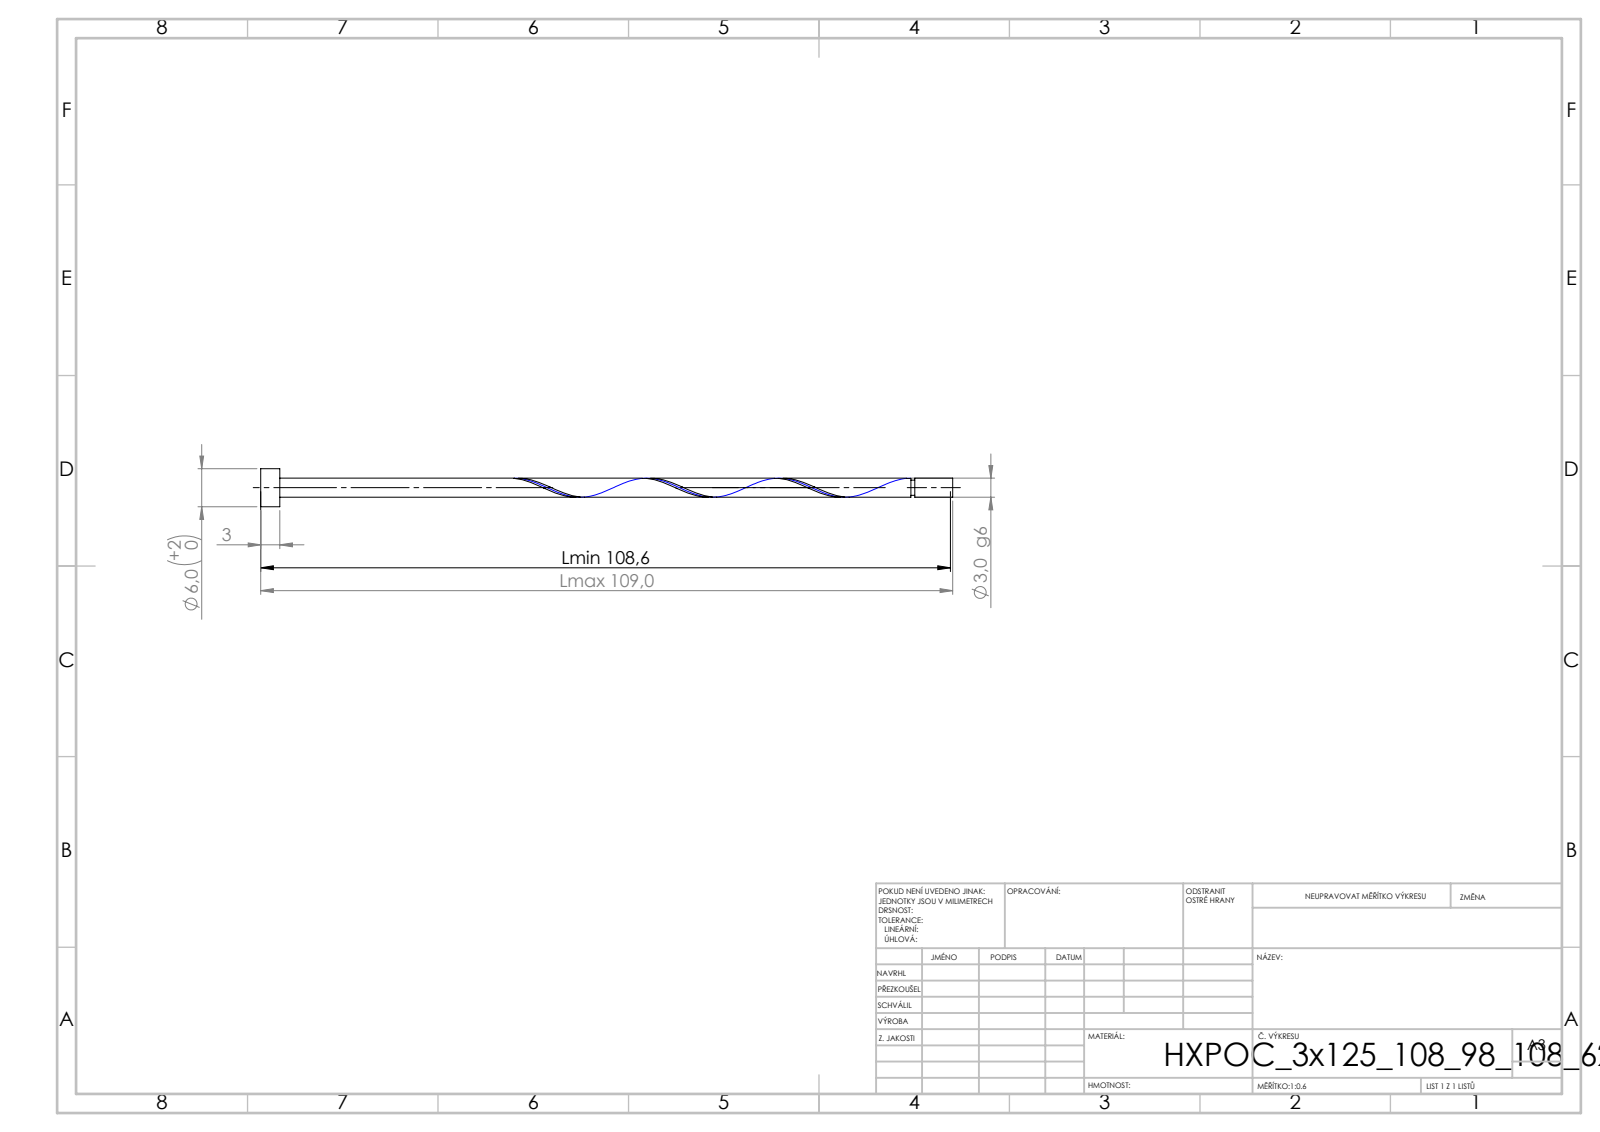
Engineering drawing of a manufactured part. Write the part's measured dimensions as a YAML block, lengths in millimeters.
step_written_by: "SolidWorks 2019 (CONFIG_CONTROL_DESIGN)"
units: millimeters
bodies: {solids: 1, faces: 21, planar: 6, cylindrical: 14, other: 1}
overall_size: [108.98, 6, 6]
volume: 824
surface_area: 1136
round_bosses_or_shafts:
  - {diameter: 6, count: 1}
  - {diameter: 3, count: 1}
  - {diameter: 2.4, count: 1}
face_to_face_distances: [3, 108.98, 105.98, 103.01, 100.01, 5.97, 102.41, 99.41, 0.6, 6.57]
